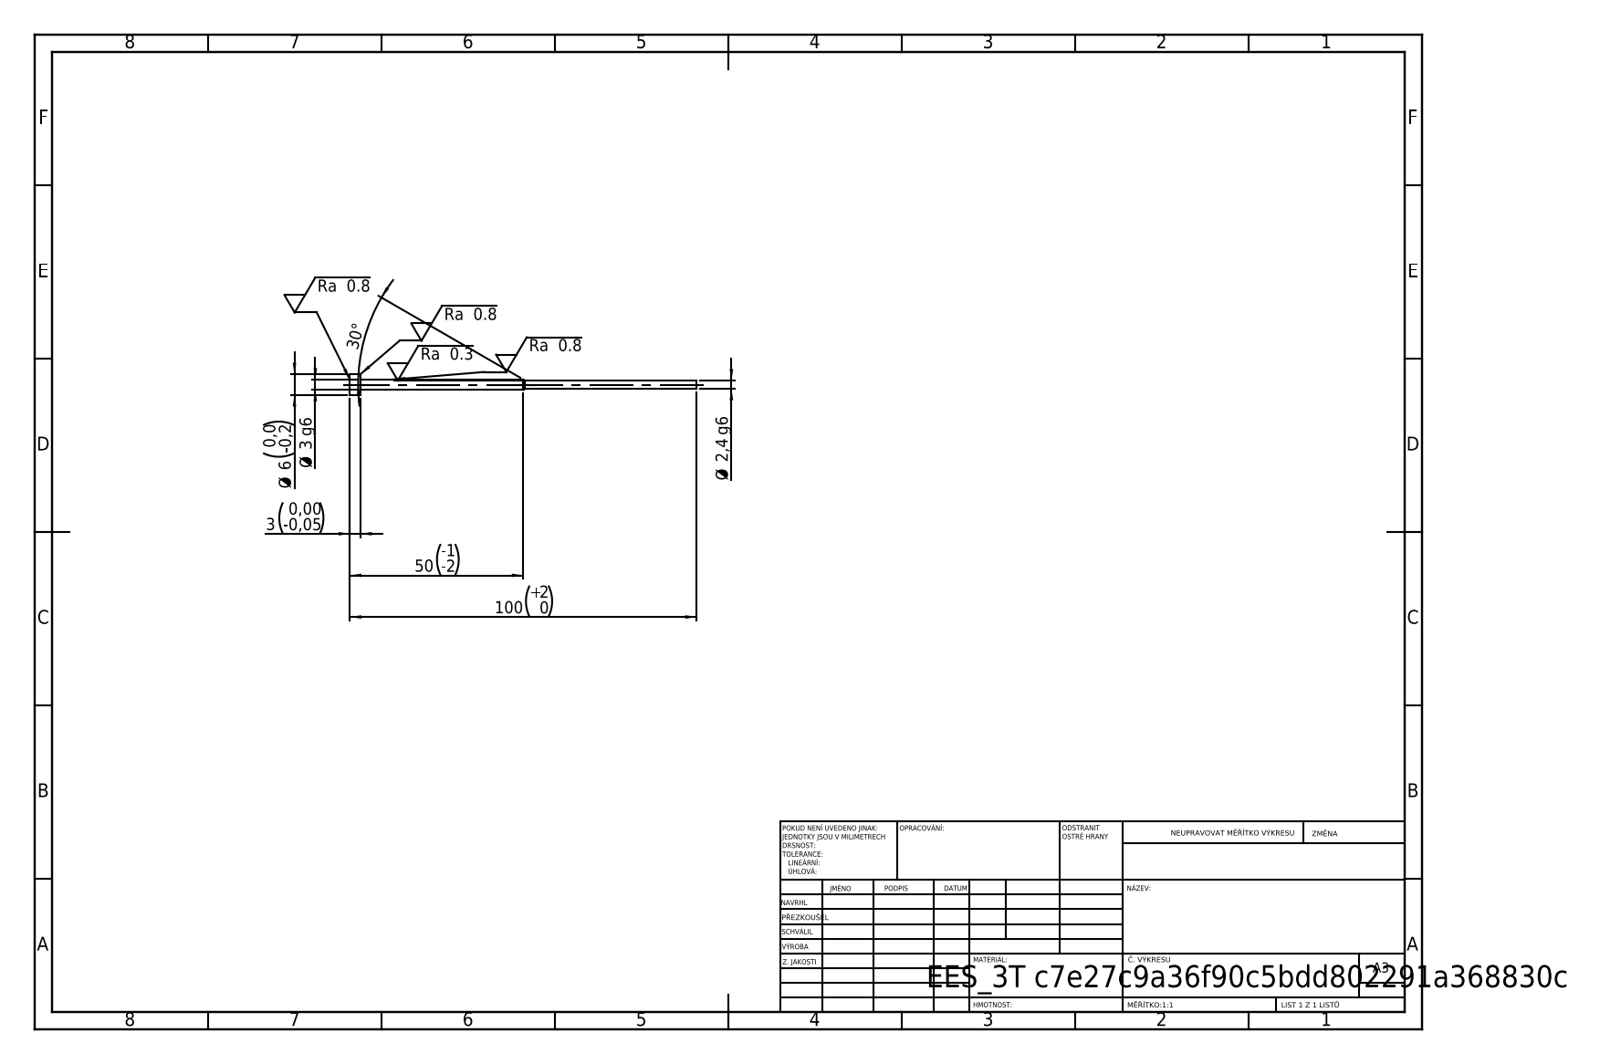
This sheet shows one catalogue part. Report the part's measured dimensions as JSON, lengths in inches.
{"step_written_by": "SolidWorks 2019 (CONFIG_CONTROL_DESIGN)", "units": "inches", "bodies": {"solids": 1, "faces": 11, "planar": 3, "cylindrical": 6, "other": 2}, "overall_size": [3.937, 0.236, 0.236], "volume_in3": 0.039, "surface_area_in2": 1.44, "round_bosses_or_shafts": [[0.236, 1], [0.118, 1], [0.094, 1]], "face_to_face_distances": [0.118, 3.819, 3.937]}
